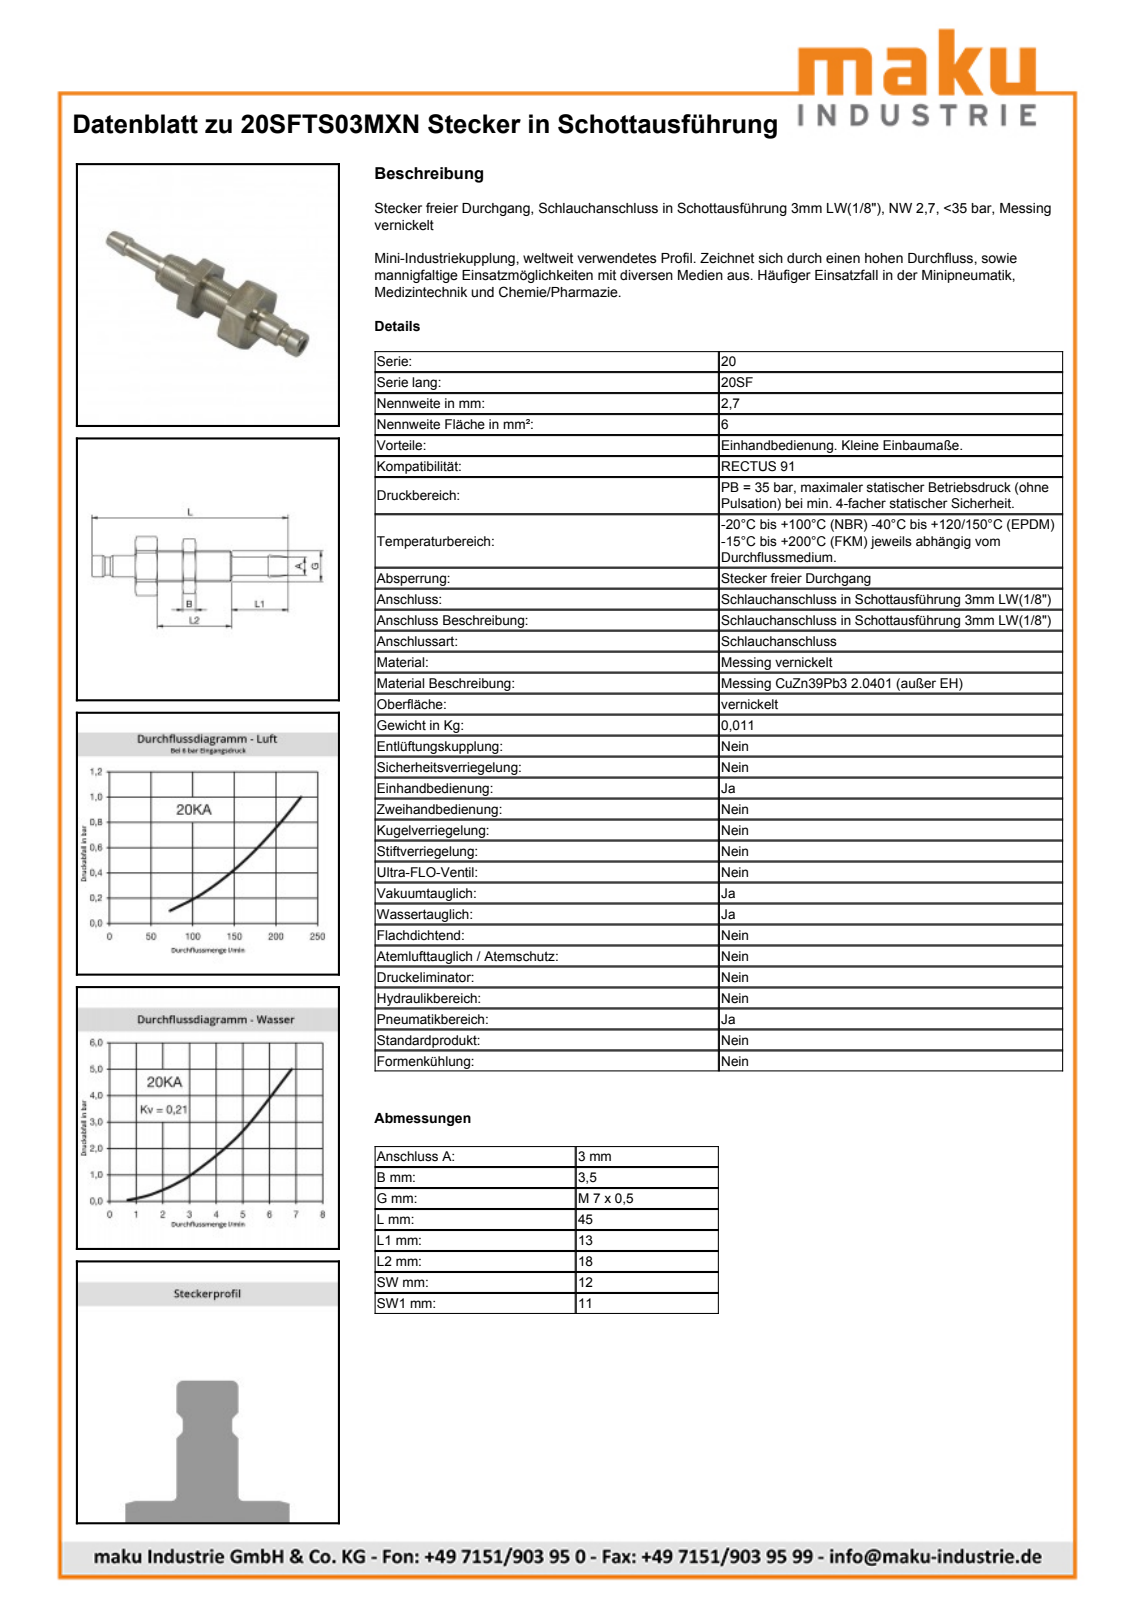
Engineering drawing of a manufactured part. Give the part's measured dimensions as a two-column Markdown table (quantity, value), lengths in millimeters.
| quantity | value |
| --- | --- |
| part name | D104240; D104206; D104103 |
| STEP written by | Autodesk Inventor 2011 (AUTOMOTIVE_DESIGN) |
| units | millimeters |
| bodies | 2 solids, 82 faces (20 planar, 22 cylindrical, 40 other) |
| overall size | 45 × 13.5 × 12 |
| volume | 1 551 mm³ |
| surface area | 1 754 mm² |
| round holes (diameter × count) | 2 × 1, 2.7 × 1, 6.46 × 1 |
| round bosses / shafts (diameter × count) | 7 × 1, 6.2 × 1, 5 × 1, 3.95 × 1, 3.1 × 1 |
| partial cylindrical surfaces (radius × count) | 6.2 × 1, 6.75 × 1 |
| main face-to-face distances | 12, 5, 5.58, 10.58, 3, 8.58, 13.58, 11, 8.42, 11.42 |
